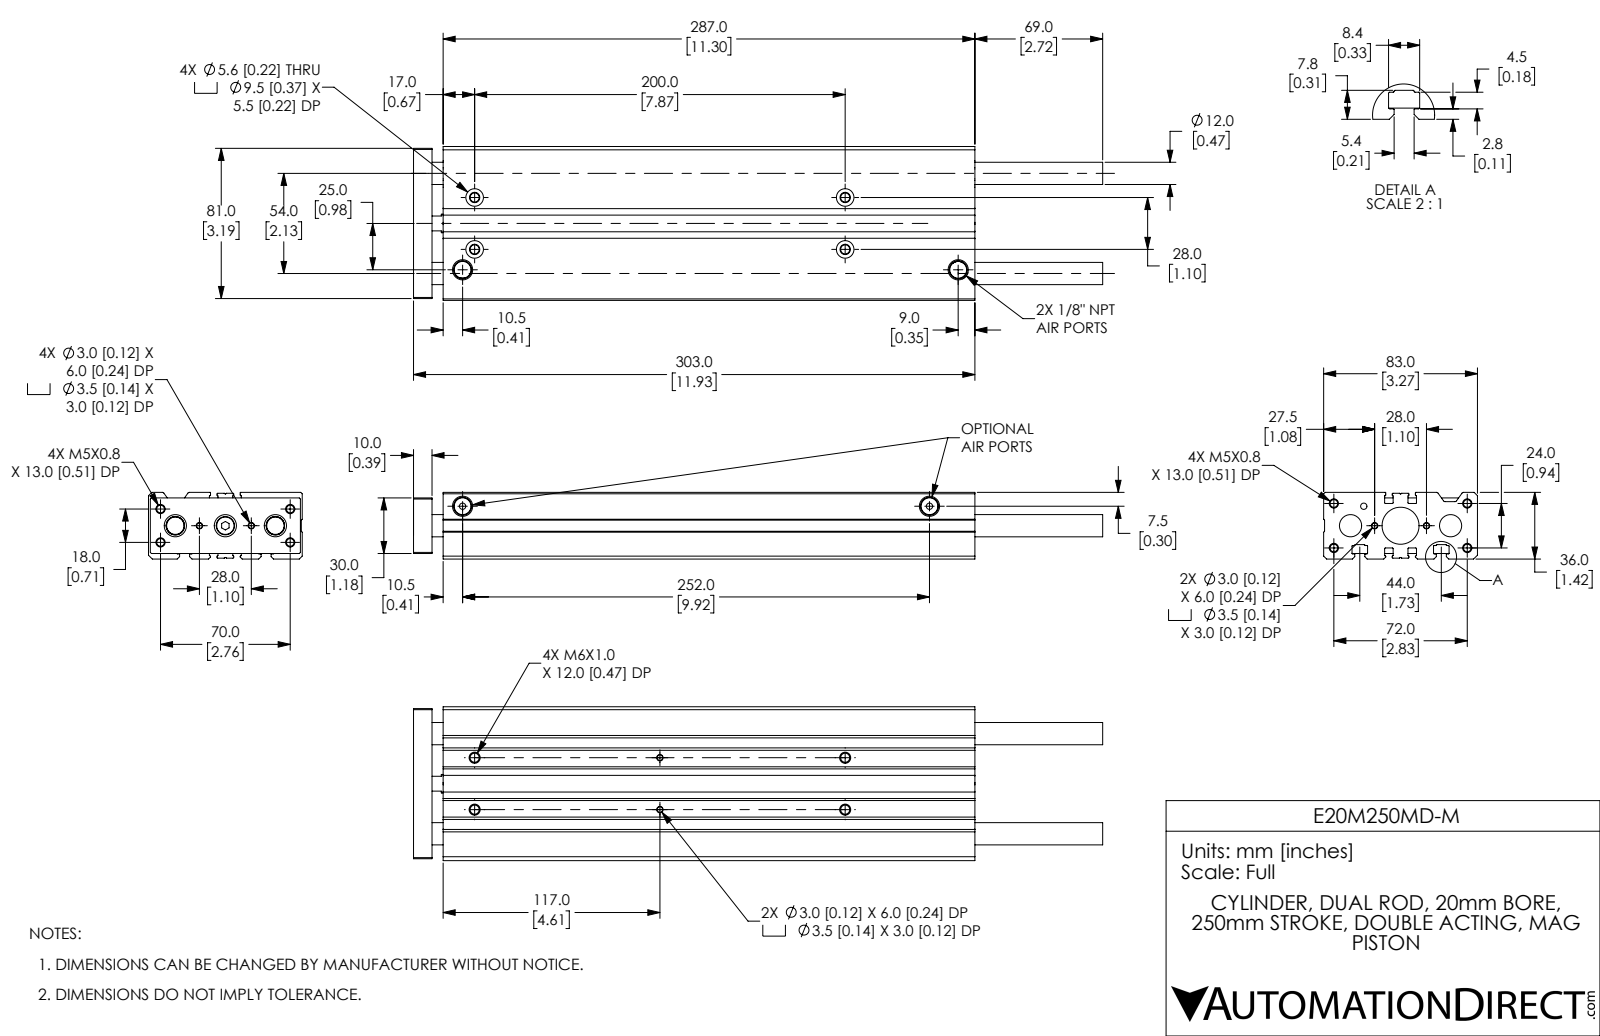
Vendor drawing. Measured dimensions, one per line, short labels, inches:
name: E20M250MD-M; E20M250MD-M_ENDPLATE; E20M250MD-M_BODY
written by: SolidWorks 2019 (CONFIG_CONTROL_DESIGN)
unit: in
bodies: 5 solids, 405 faces (128 planar, 182 cylindrical, 95 other)
size: 14.646 × 3.268 × 1.417
volume: 45.65 in³; area: 296.4 in²
holes: 8× ⌀0.163, 4× ⌀0.118, 4× ⌀0.138, 4× ⌀0.194, 4× ⌀0.22, 4× ⌀0.374, 3× ⌀0.236, 3× ⌀0.472, 2× ⌀0.135, 2× ⌀0.39, 1× ⌀0.135, 1× ⌀0.472
bosses: 1× ⌀0.394, 1× ⌀0.39
rounds: 20× R0.016, 18× R0.008, 10× R0.012, 8× R0.01, 4× R0.039
face distances: 1.417, 0.02, 3.268, 0.236, 1.181, 1.791, 0.874, 1.11, 1.476, 1.295
hole spacings: 0.124, 0.474, 0.591, 0.828, 0.9, 0.987, 1.102, 1.423
